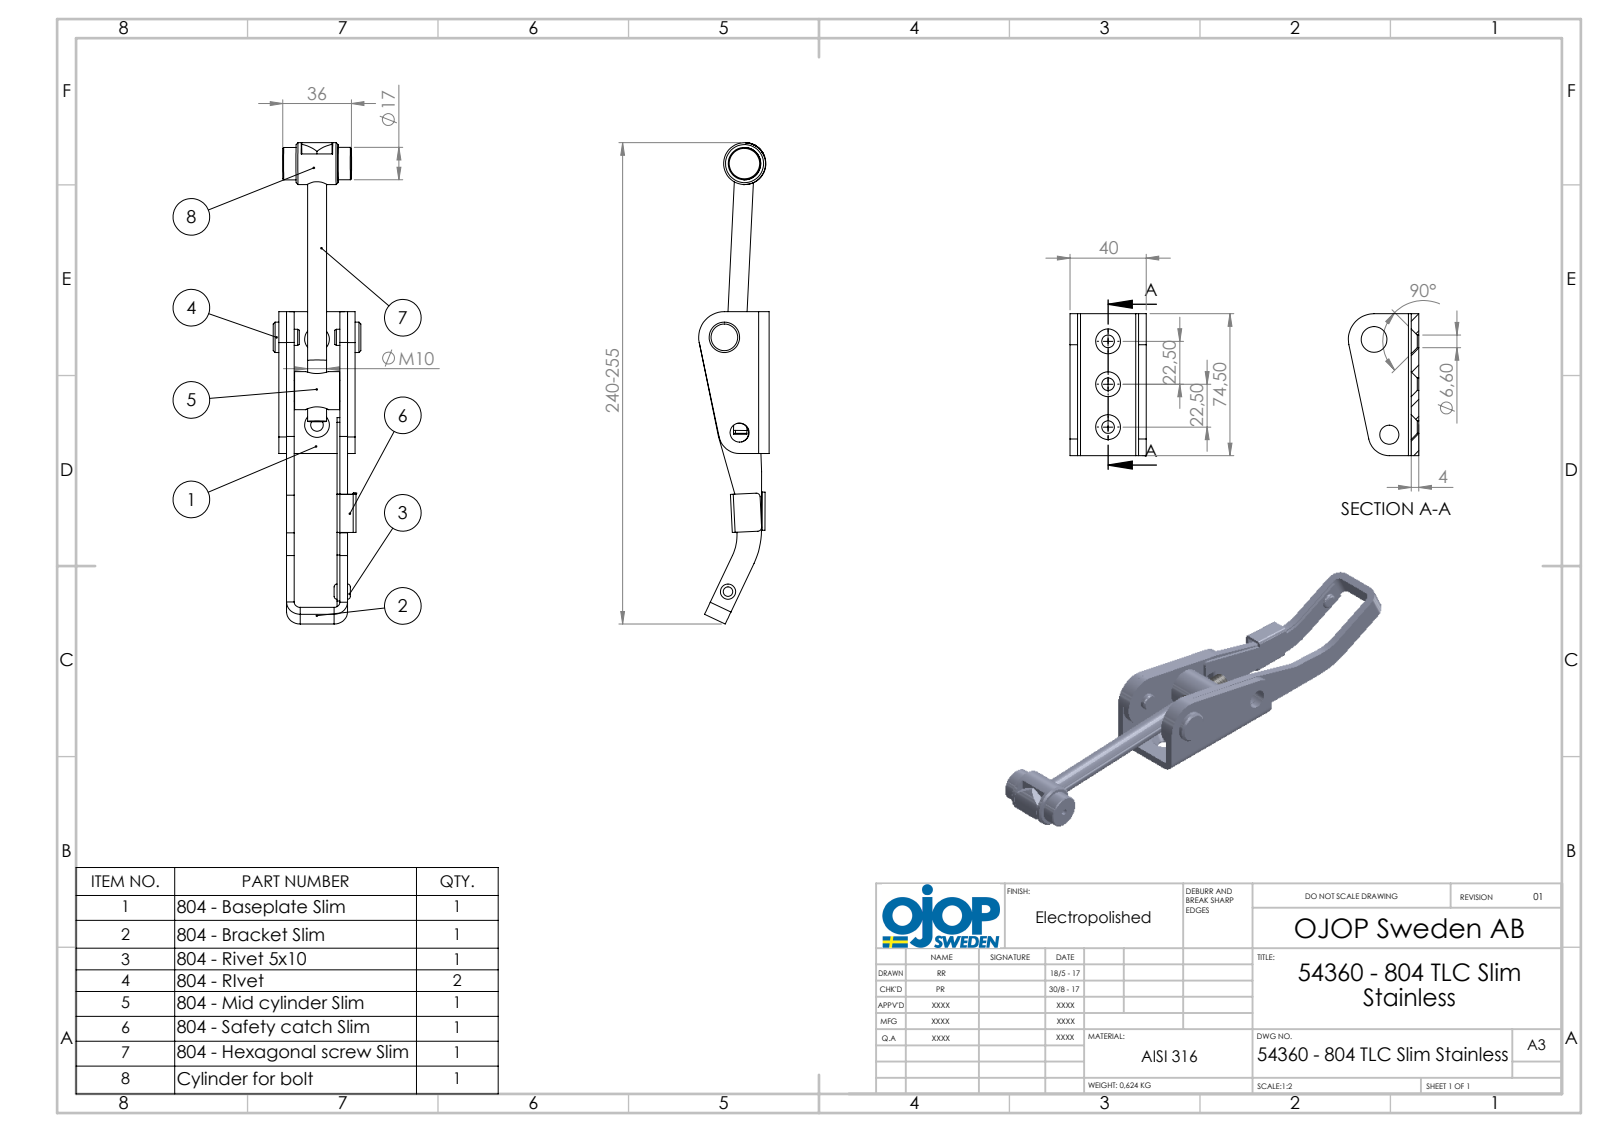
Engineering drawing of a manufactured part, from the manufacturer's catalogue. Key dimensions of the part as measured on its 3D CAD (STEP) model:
Part name (STEP PRODUCT): 62080 - Rulle 804 Slim; 62035 - Ansatsnit 10,9x5,7x8,5x8,0 FZB(804); 74132 - Säkerhetsspärr 804 Slim; 72297 - Platta 804 Slim (+5 more)
STEP written by: SolidWorks 2015 (AUTOMOTIVE_DESIGN)
Units: millimetres
Bodies: 9 solids, 234 faces (100 planar, 100 cylindrical, 34 other)
Overall size (bounding box): 252.62 × 46 × 37
Volume: 80 910 mm³ · Surface area: 47 399 mm²
Round holes (diameter × count): ⌀6.6 ×3, ⌀10 ×2, ⌀3.3 ×1, ⌀4.97 ×1, ⌀5.1 ×1, ⌀8.6 ×1, ⌀9.3 ×1, ⌀10.3 ×1, ⌀11.2 ×1, ⌀13.5 ×1
Round bosses / shafts (diameter × count): ⌀17 ×2, ⌀22 ×1, ⌀20 ×1, ⌀16 ×1, ⌀11 ×1, ⌀10.9 ×1, ⌀10.01 ×1, ⌀10 ×1
Partial cylindrical surfaces — rounded edges, fillets, slot ends (radius × count): R1.5 ×6, R0.5 ×4, R2 ×4, R5.5 ×2, R3 ×1, R3.17 ×1, R7 ×1, R7.17 ×1
Main face-to-face distances: 4, 32, 28, 36, 8, 24, 1.5, 40, 5.5, 9.5
Hole centre spacings: 22.5, 22.23, 22.27, 28.41, 45, 50.64, 50.66, 83.58
